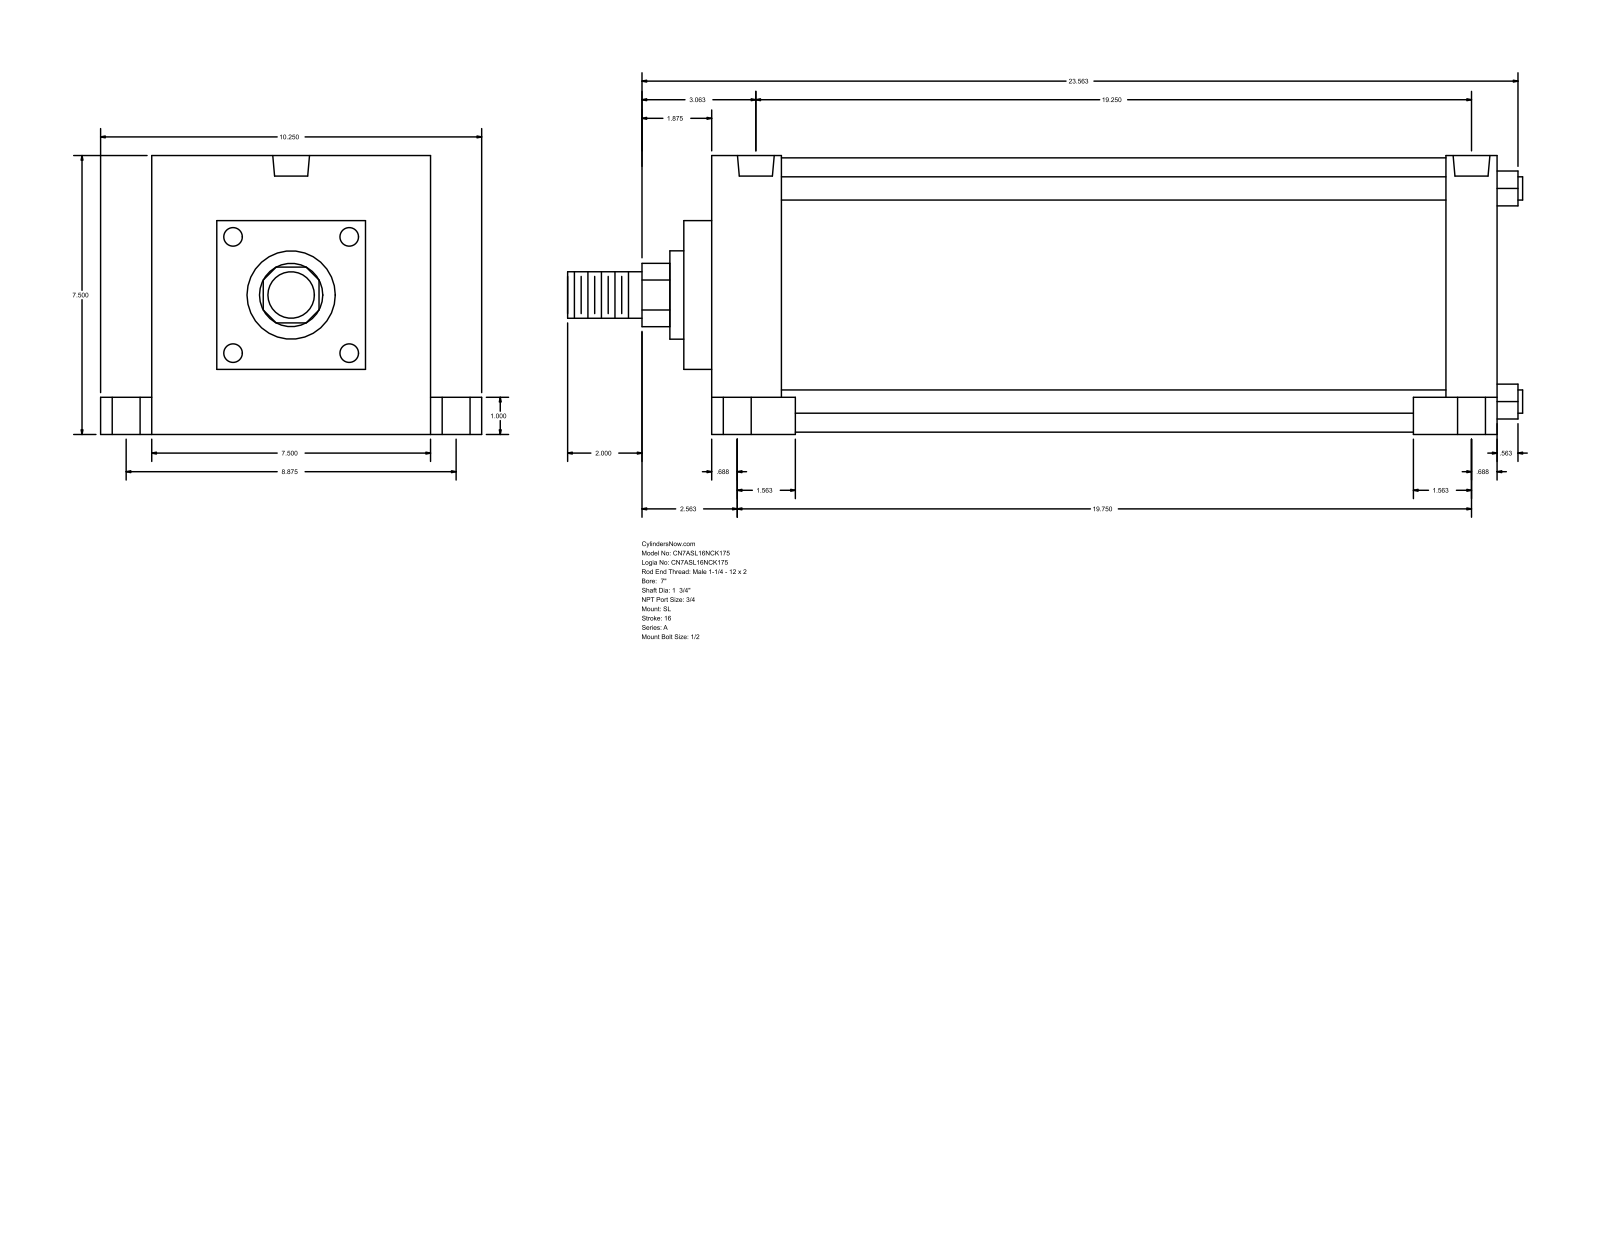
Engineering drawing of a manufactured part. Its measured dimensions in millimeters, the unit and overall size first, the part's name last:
Units: millimetres
Overall size (bounding box): 652.46 × 260.35 × 190.5
Round holes (diameter × count): ⌀15.08 ×4, ⌀19.05 ×4, ⌀25.4 ×4, ⌀25.12 ×2
Round bosses / shafts (diameter × count): ⌀15.88 ×4, ⌀187.32 ×1, ⌀60.33 ×1, ⌀44.45 ×1, ⌀31.75 ×1
Partial cylindrical surfaces — rounded edges, fillets, slot ends (radius × count): R21.63 ×1
Main face-to-face distances: 190.5, 536.58, 34.93, 19.05, 146.05, 47.63, 488.95, 501.65, 454.02, 44.45
Hole centre spacings: 5.56, 112.71, 112.85, 113.42, 114.18, 225.42, 477.83, 483.39
Bodies: 0 solids, 117 faces (85 planar, 32 cylindrical, 0 other)
Part name (STEP PRODUCT): A_SL__0700_1.75
STEP written by: GSSL Pune (CONFIG_CONTROL_DESIGN)
